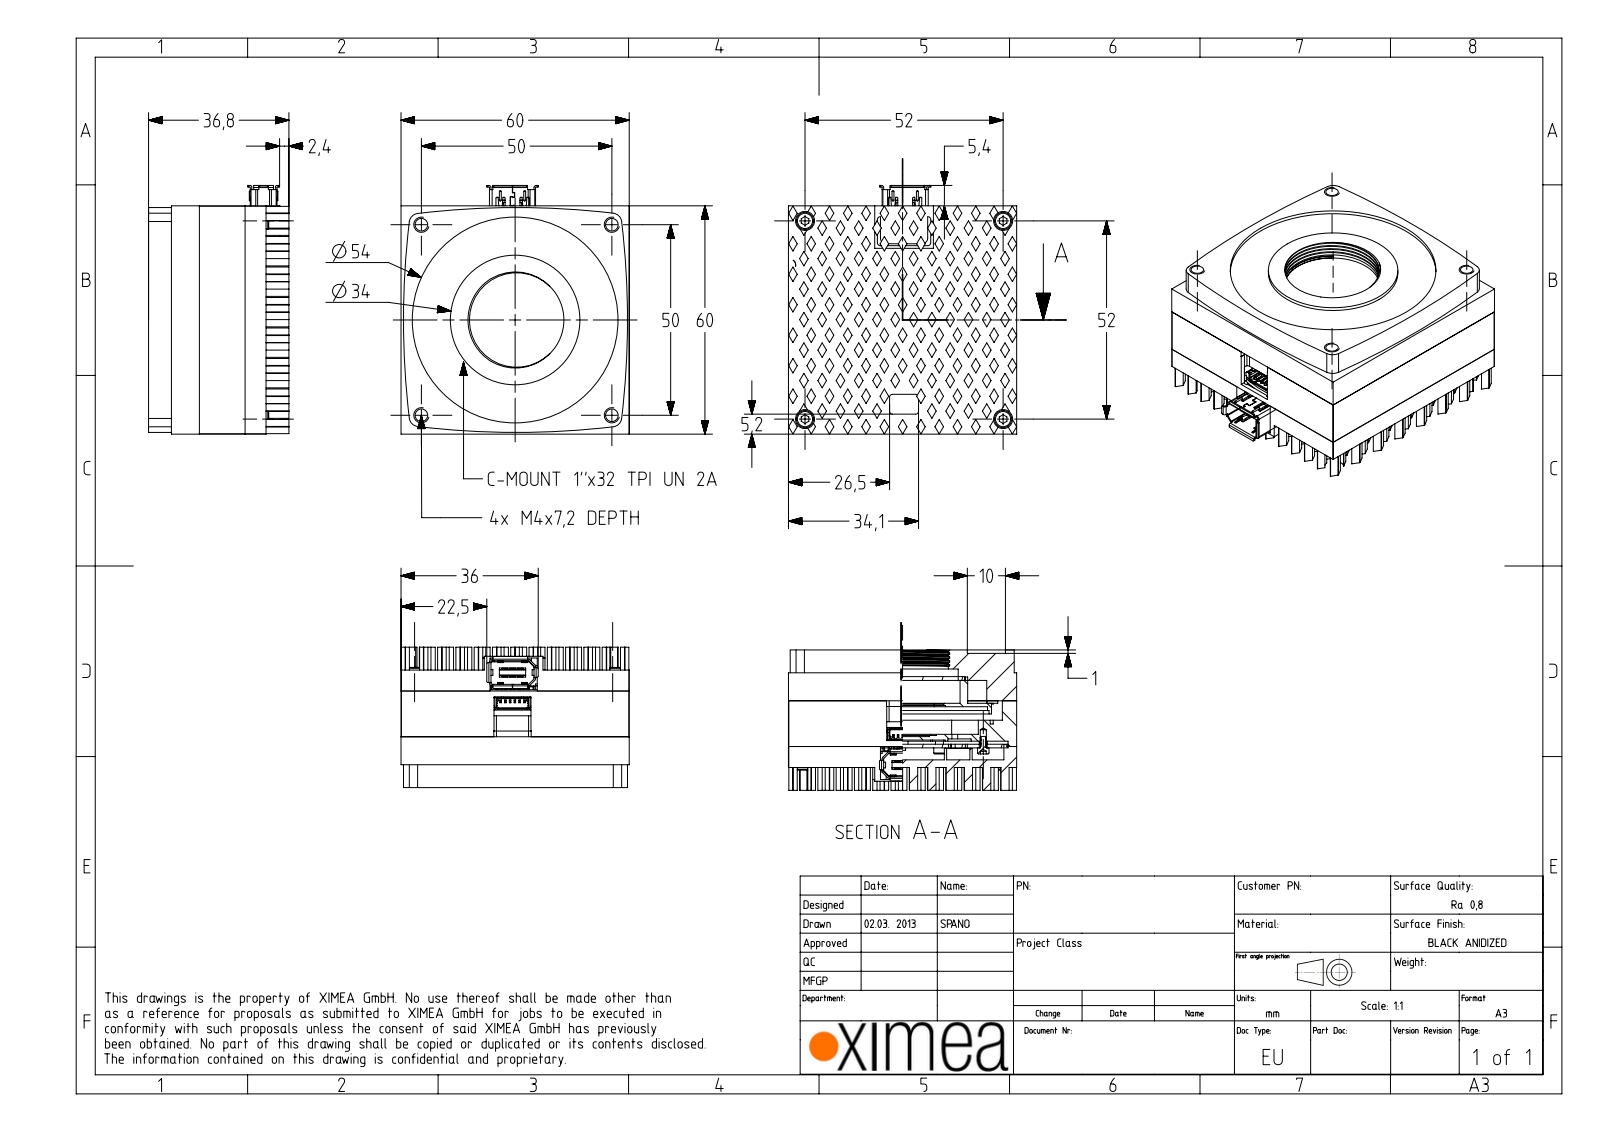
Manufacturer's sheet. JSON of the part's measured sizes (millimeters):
{"part_name": "FLT_BK7_AR2X_D32_sldprt; MECH_MR_FLTHOLD_4021_VE_sldprt; din912_M2.5x20; din912_M1.6x3mm (+8 more)", "step_written_by": "SIEMENS PLM Software NX 8.5 (AUTOMOTIVE_DESIGN)", "units": "millimeters", "bodies": {"solids": 21, "faces": 2904, "planar": 2373, "cylindrical": 455, "other": 76}, "overall_size": [65.25, 59.91, 36.84], "volume_mm3": 78111, "surface_area_mm2": 60252, "round_holes": [[0.95, 36], [1.5, 34], [0.5, 26], [2.1, 8], [5.4, 8], [1.25, 6], [1.6, 6], [2.05, 4], [2.5, 4], [3.3, 4], [4, 4], [5, 4]], "round_bosses_or_shafts": [[3, 6], [2.1, 6], [4.5, 4], [54, 1], [50.8, 1], [47, 1], [46.1, 1], [44.6, 1]], "partial_cylinders_radius": [[0.25, 30], [0.75, 19], [1.5, 17], [0.4, 13], [0.1, 12], [0.5, 10], [0.55, 8], [0.7, 8]], "face_to_face_distances": [5.5, 6.1, 0.6, 2, 22.84, 59.9, 17.5, 6, 6.9, 14], "hole_center_spacings": [25.71, 1.78, 26.2, 3.56, 25.65, 25.9, 26.62, 5.34]}
